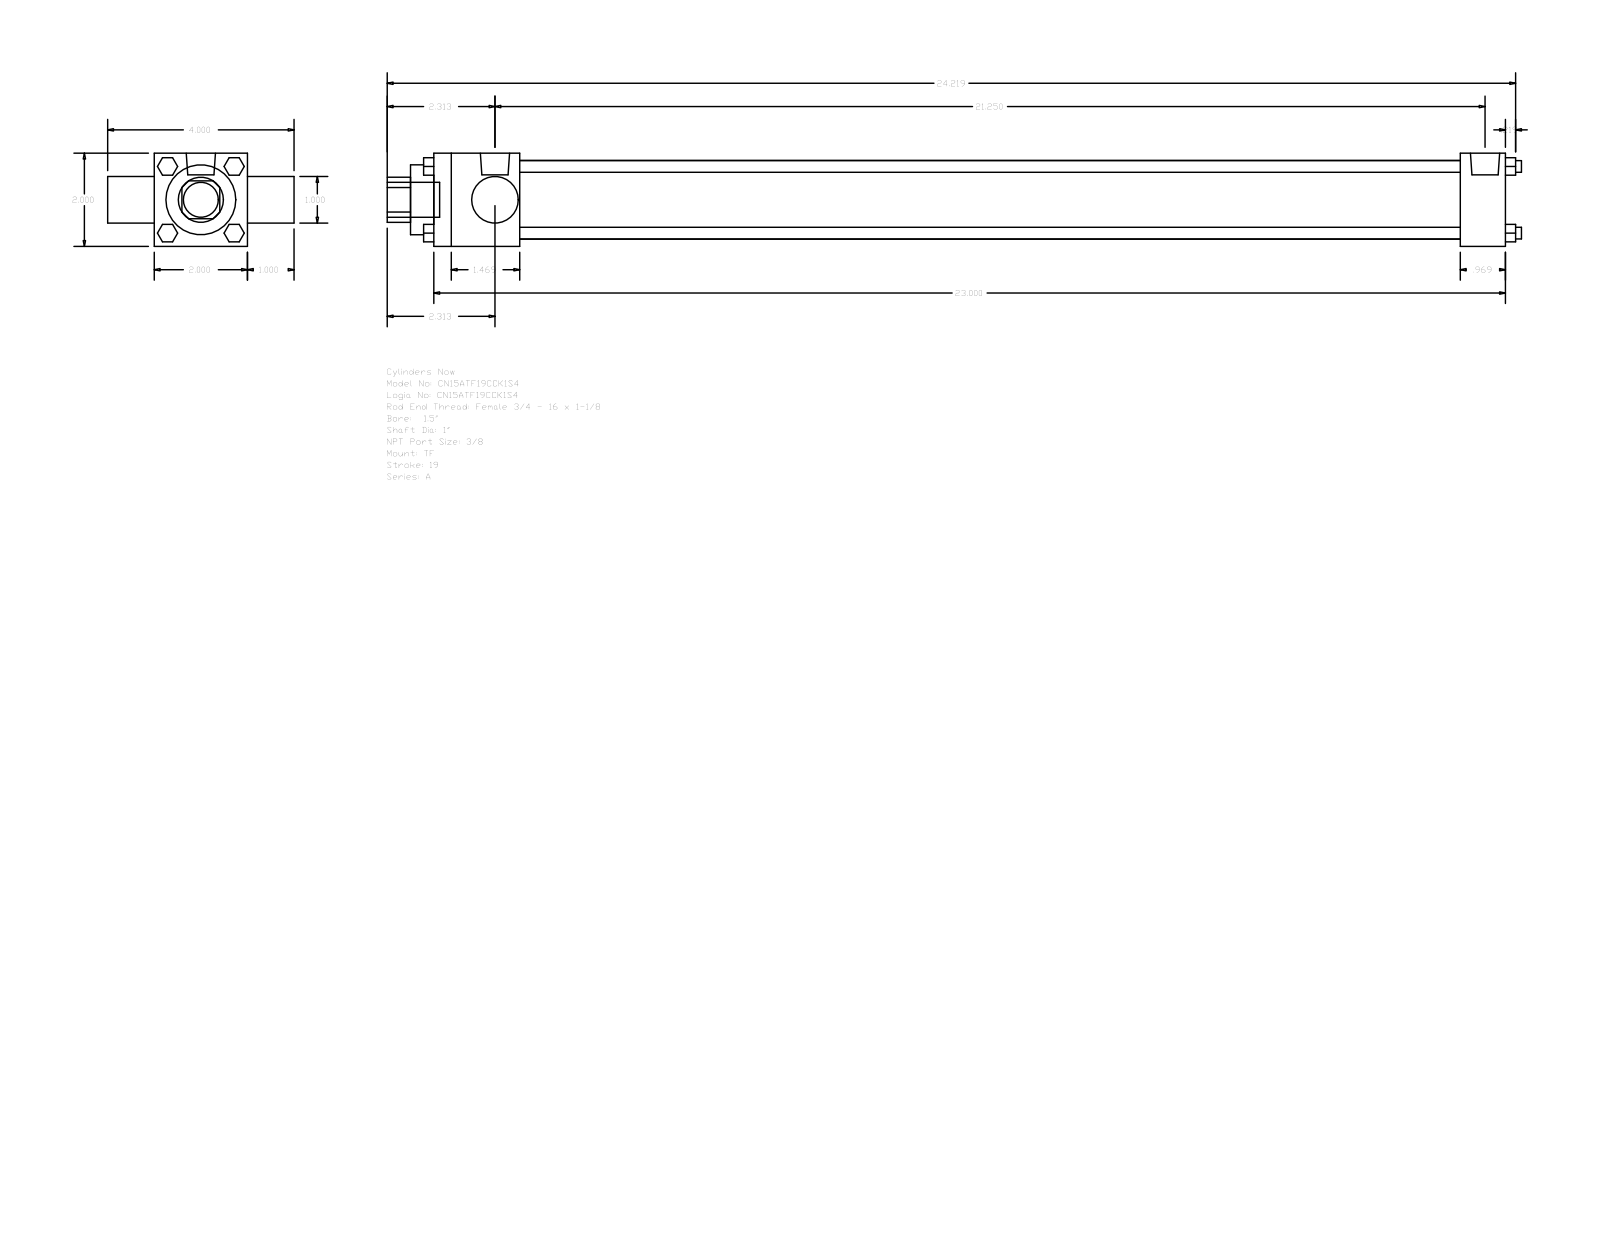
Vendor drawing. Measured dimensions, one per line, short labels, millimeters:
name: A_TF__0150_1
written by: GSSL Pune (CONFIG_CONTROL_DESIGN)
unit: mm
bodies: 0 solids, 120 faces (92 planar, 28 cylindrical, 0 other)
size: 618.33 × 101.6 × 50.8
holes: 2× ⌀25.4, 1× ⌀38.1, 1× ⌀42.93
bosses: 4× ⌀6.35, 3× ⌀5.56, 2× ⌀15.93, 1× ⌀19.05
rounds: 1× R12.29
face distances: 50.8, 25.4, 584.2, 76.2, 46.83, 559.59, 512.76, 537.37, 24.61, 12.7
